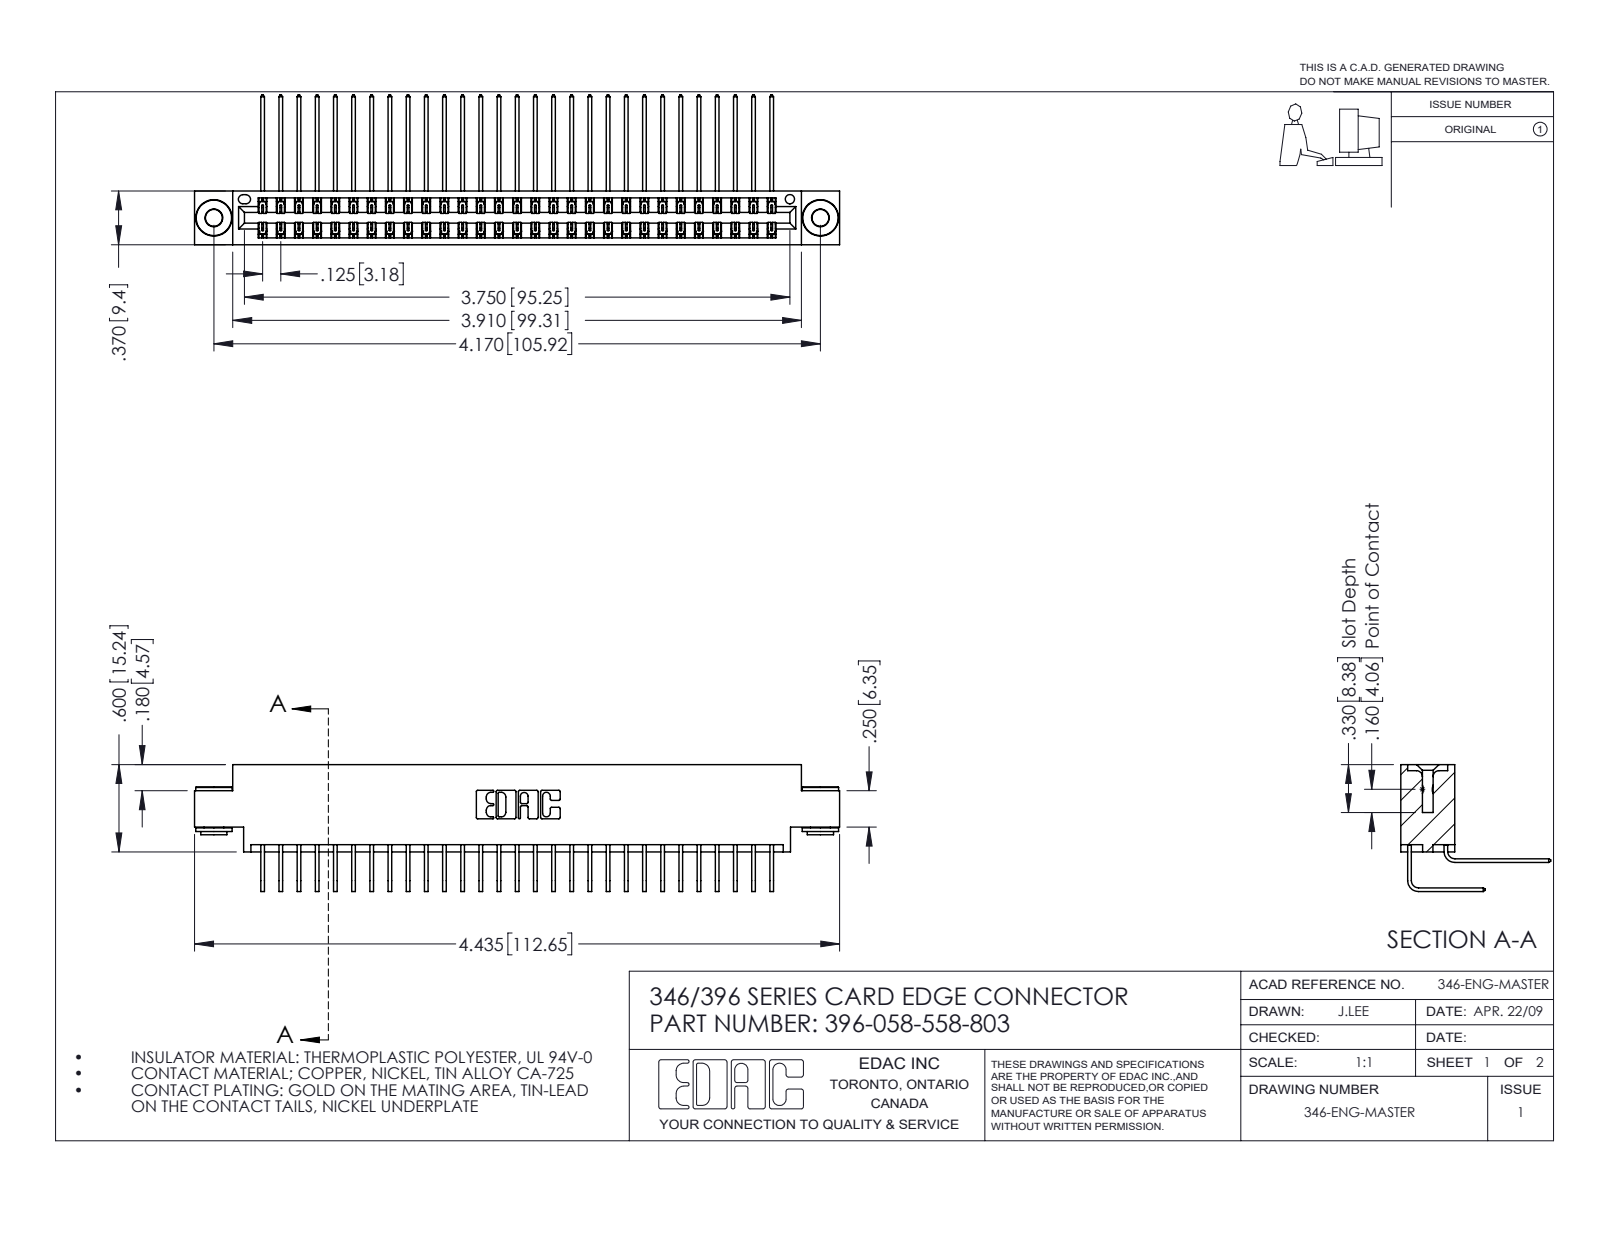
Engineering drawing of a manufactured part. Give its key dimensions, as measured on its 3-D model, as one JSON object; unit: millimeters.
{"part_name": "396-058-558-803; 345-250-002_345-250-002-102; 345-292-001_558 Tail - 2; 346 Part_0.170 Offset - 0.156 Dia-TH (+1 more)", "step_written_by": "SolidWorks 2016 (CONFIG_CONTROL_DESIGN)", "units": "millimeters", "bodies": {"solids": 61, "faces": 3296, "planar": 2236, "cylindrical": 1052, "other": 8}, "overall_size": [112.6, 26.2, 22.2], "volume_mm3": 11100, "surface_area_mm2": 17030, "round_holes": [[2.9, 2], [4, 2], [1.6, 1]], "round_bosses_or_shafts": [[6.4, 2], [4.6, 2], [3.5, 2]], "partial_cylinders_radius": [[0.2, 87], [0.3, 22], [0.2, 6], [0.8, 6], [0.7, 3], [0.4, 2], [0.6, 2], [0.6, 2]], "face_to_face_distances": [8.2, 1.2, 0.6, 9.4, 6.4, 7.6, 1.8, 7, 3.8, 5.6], "hole_center_spacings": [6.2, 100.6, 105.9]}
